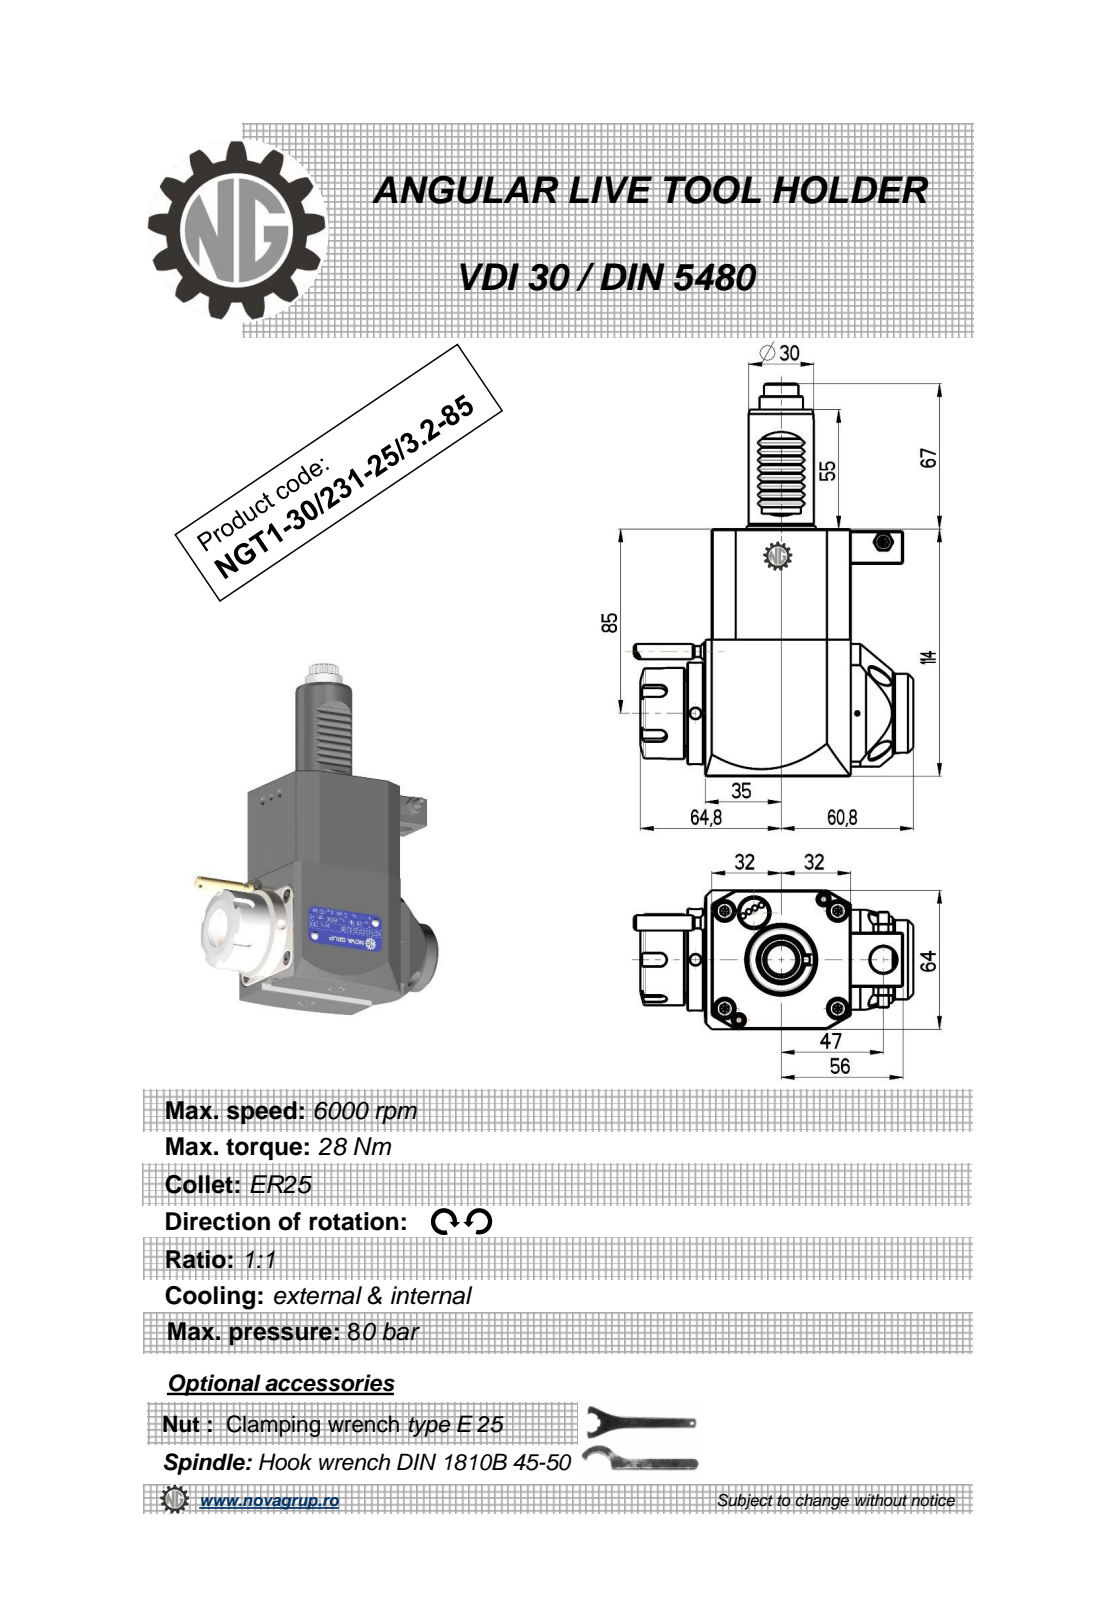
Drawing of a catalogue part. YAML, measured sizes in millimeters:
part_name: "NGT1_30_231_25_3_2_85"
step_written_by: "PRO/ENGINEER BY PARAMETRIC TECHNOLOGY CORPORATION, 2010280 (CONFIG_CONTROL_DESIGN)"
units: millimeters
bodies: {solids: 1, faces: 507, planar: 186, cylindrical: 155, other: 166}
overall_size: [181, 128.63, 64]
volume: 599323
surface_area: 56791
round_holes:
  - {diameter: 5, count: 2}
  - {diameter: 2.5, count: 1}
  - {diameter: 3, count: 1}
  - {diameter: 4.2, count: 1}
  - {diameter: 9.5, count: 1}
  - {diameter: 12, count: 1}
  - {diameter: 20.3, count: 1}
round_bosses_or_shafts:
  - {diameter: 8.96, count: 2}
  - {diameter: 5, count: 2}
  - {diameter: 47, count: 1}
  - {diameter: 42, count: 1}
  - {diameter: 36.5, count: 1}
  - {diameter: 35, count: 1}
  - {diameter: 30, count: 1}
  - {diameter: 20, count: 1}
partial_cylinders:
  - {radius: 1.98, count: 36}
  - {radius: 0.26, count: 12}
  - {radius: 0.3, count: 8}
  - {radius: 3, count: 5}
  - {radius: 160, count: 2}
  - {radius: 7.08, count: 1}
  - {radius: 7.92, count: 1}
  - {radius: 13, count: 1}
face_to_face_distances: [64, 114, 0.5, 67, 3.2, 67.2, 76.42, 7.5, 3, 8]
hole_center_spacings: [33.19, 50.92, 76.5, 86.45, 117.11]
